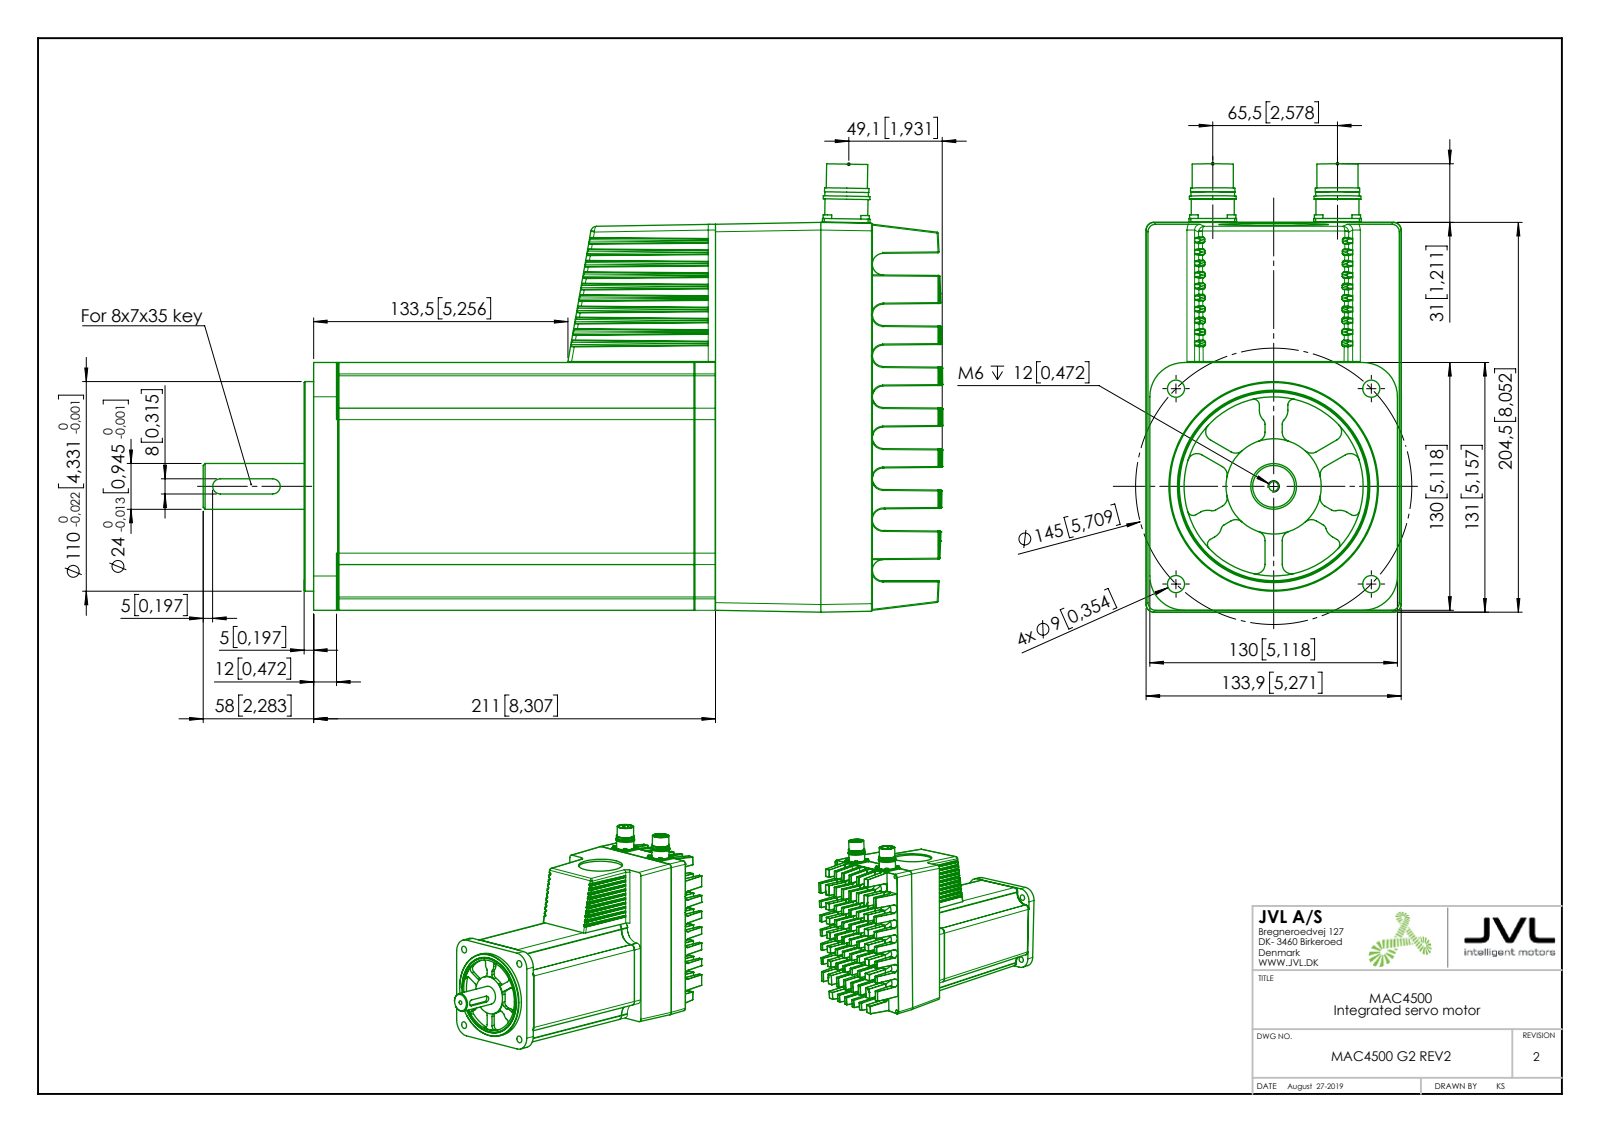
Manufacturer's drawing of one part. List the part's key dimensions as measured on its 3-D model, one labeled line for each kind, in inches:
Part name (STEP PRODUCT): Rear flange S; M23 female; Center part S_MAC 4500; Shaft S (+6 more)
STEP written by: SolidWorks 2018 (AUTOMOTIVE_DESIGN)
Units: inches
Bodies: 9 solids, 2443 faces (757 planar, 981 cylindrical, 705 other)
Overall size (bounding box): 15.287 × 9.263 × 5.271
Volume: 367.5 in³ · Surface area: 792.4 in²
Round holes (diameter × count): ⌀0.098 ×8, ⌀0.079 ×5, ⌀0.169 ×4, ⌀0.354 ×4, ⌀0.787 ×2, ⌀0.795 ×2, ⌀0.181 ×1, ⌀0.197 ×1, ⌀2.269 ×1, ⌀3.701 ×1, ⌀3.937 ×1, ⌀4.606 ×1
Round bosses / shafts (diameter × count): ⌀0.177 ×8, ⌀0.079 ×4, ⌀0.965 ×2, ⌀0.917 ×2, ⌀0.902 ×2, ⌀0.89 ×2, ⌀0.85 ×2, ⌀4.409 ×1
Partial cylindrical surfaces — rounded edges, fillets, slot ends (radius × count): R0.02 ×297, R0.012 ×90, R0.031 ×40, R0.197 ×18, R0.118 ×15, R0.157 ×12, R0.024 ×10, R0.236 ×8
Main face-to-face distances: 2.177, 5.118, 7.362, 7.795, 9.972, 0.433, 2.61, 0.846, 1.891, 7.874
Hole centre spacings: 0.557, 0.787, 2.578, 0.236, 0.278, 1.113, 2.219, 2.696
